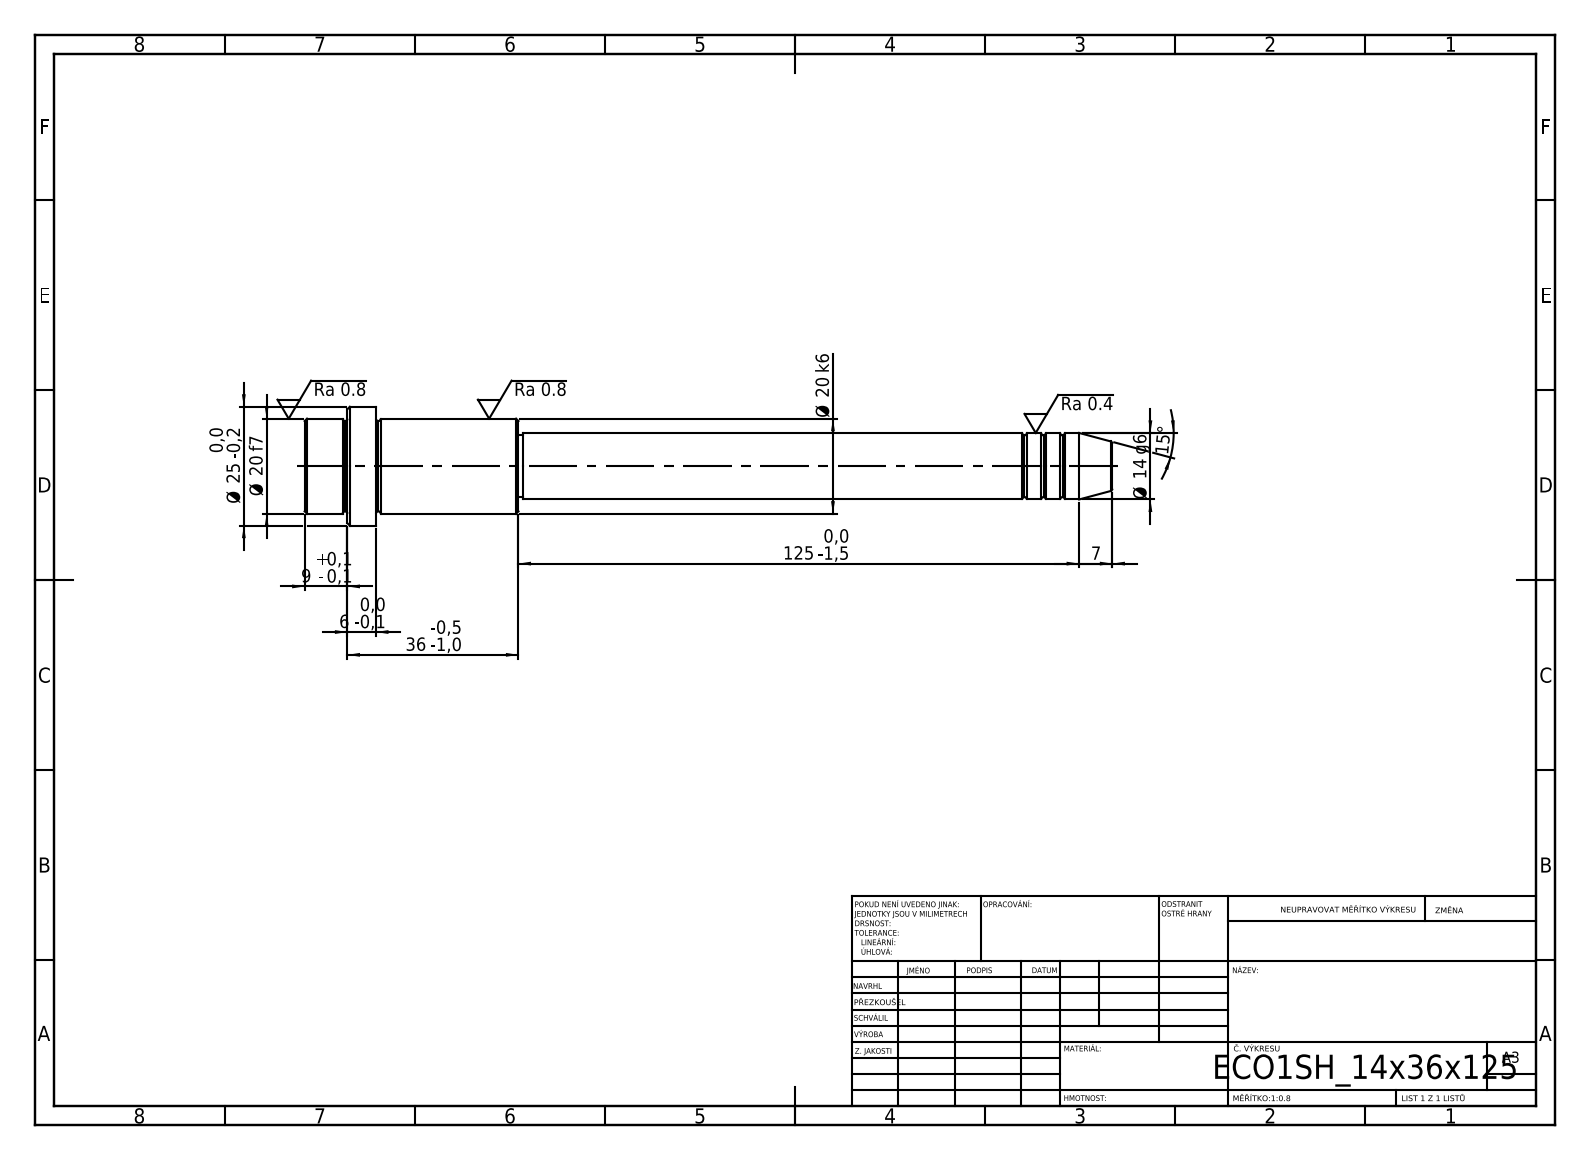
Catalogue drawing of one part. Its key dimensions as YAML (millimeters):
step_written_by: "SolidWorks 2019 (CONFIG_CONTROL_DESIGN)"
units: millimeters
bodies: {solids: 1, faces: 52, planar: 6, cylindrical: 16, other: 30}
overall_size: [170, 25, 25]
volume: 34031
surface_area: 9404
round_bosses_or_shafts:
  - {diameter: 25, count: 1}
  - {diameter: 20, count: 1}
  - {diameter: 14, count: 1}
  - {diameter: 13, count: 1}
face_to_face_distances: [15, 30, 45, 36, 6, 9, 125, 155, 161, 170]
